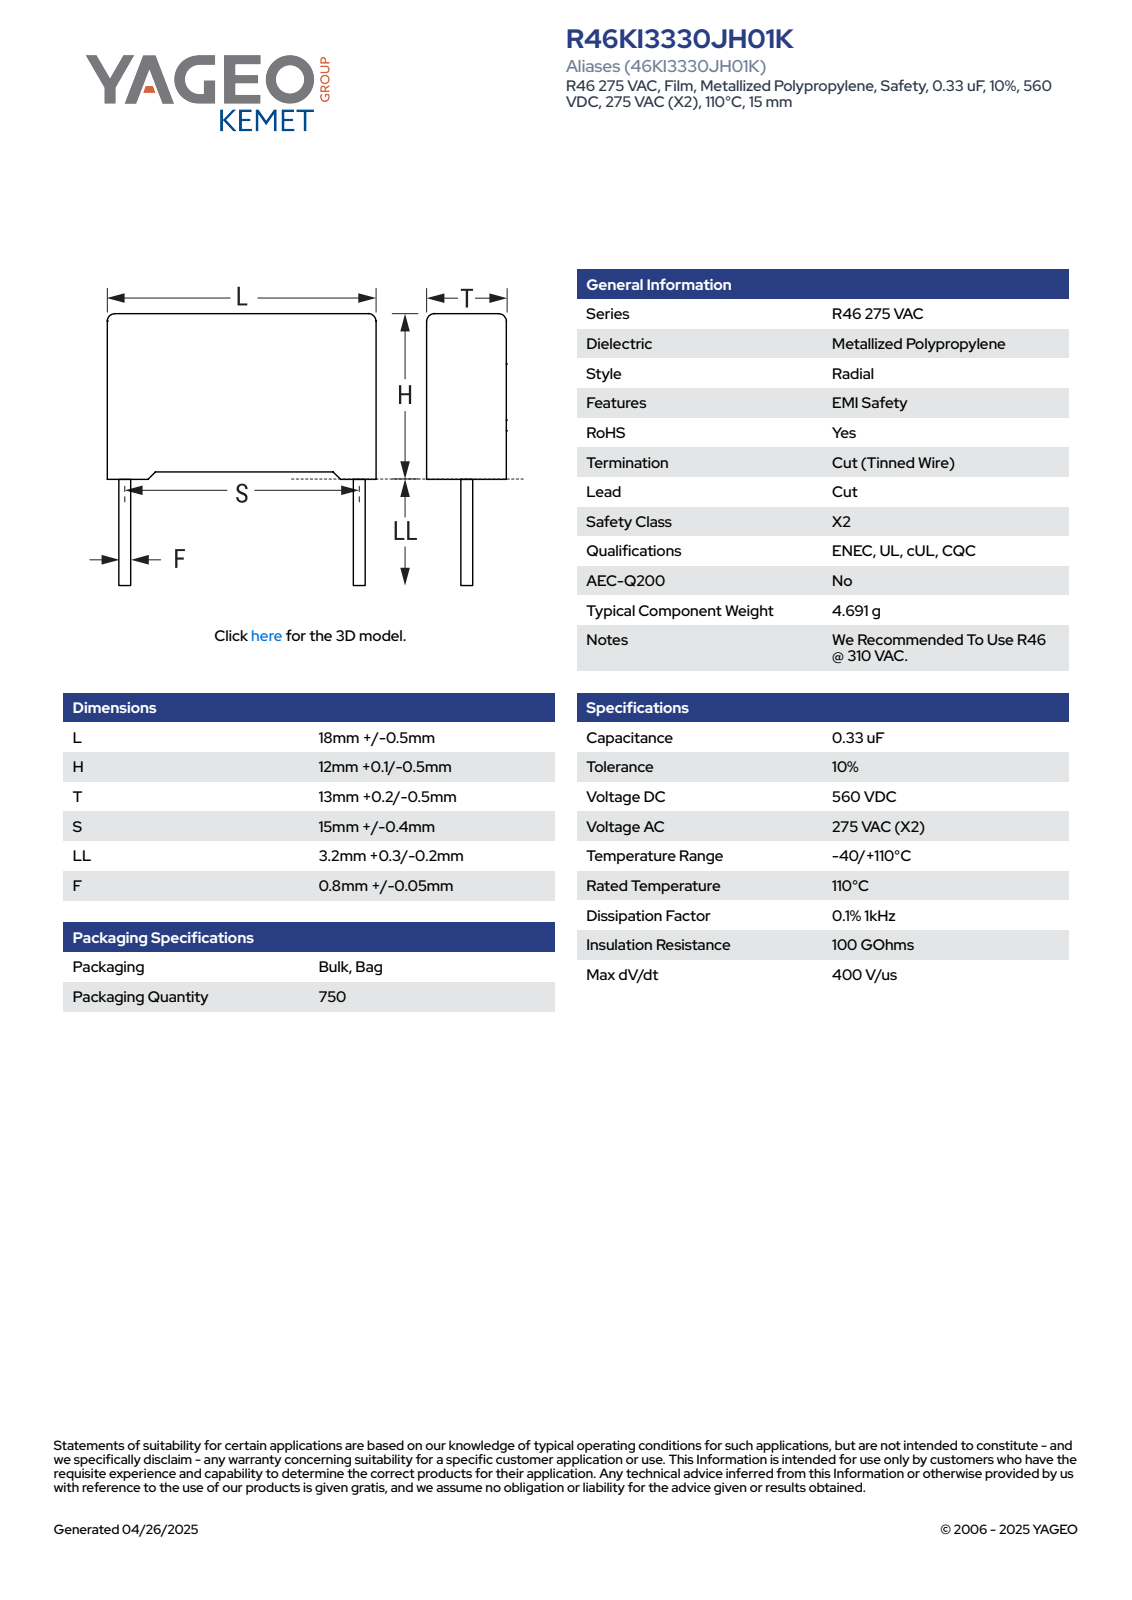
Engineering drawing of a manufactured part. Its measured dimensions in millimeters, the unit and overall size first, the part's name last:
Units: millimetres
Overall size (bounding box): 18.5 × 15.6 × 13.21
Round bosses / shafts (diameter × count): ⌀0.85 ×2
Partial cylindrical surfaces — rounded edges, fillets, slot ends (radius × count): R0.5 ×4
Main face-to-face distances: 13.2, 11.35, 18.5, 0.62, 0.75, 12.1, 17.88, 12.58, 0.42, 0.33
Volume: 2 795 mm³ · Surface area: 1 315 mm²
Bodies: 4 solids, 85 faces (77 planar, 8 cylindrical, 0 other)
Part name (STEP PRODUCT): CFR_RB2_18X12X13_L18.5H12.1T13.2S15LL3.5F0.85
STEP written by: SolidWorks 2021 (AUTOMOTIVE_DESIGN)
